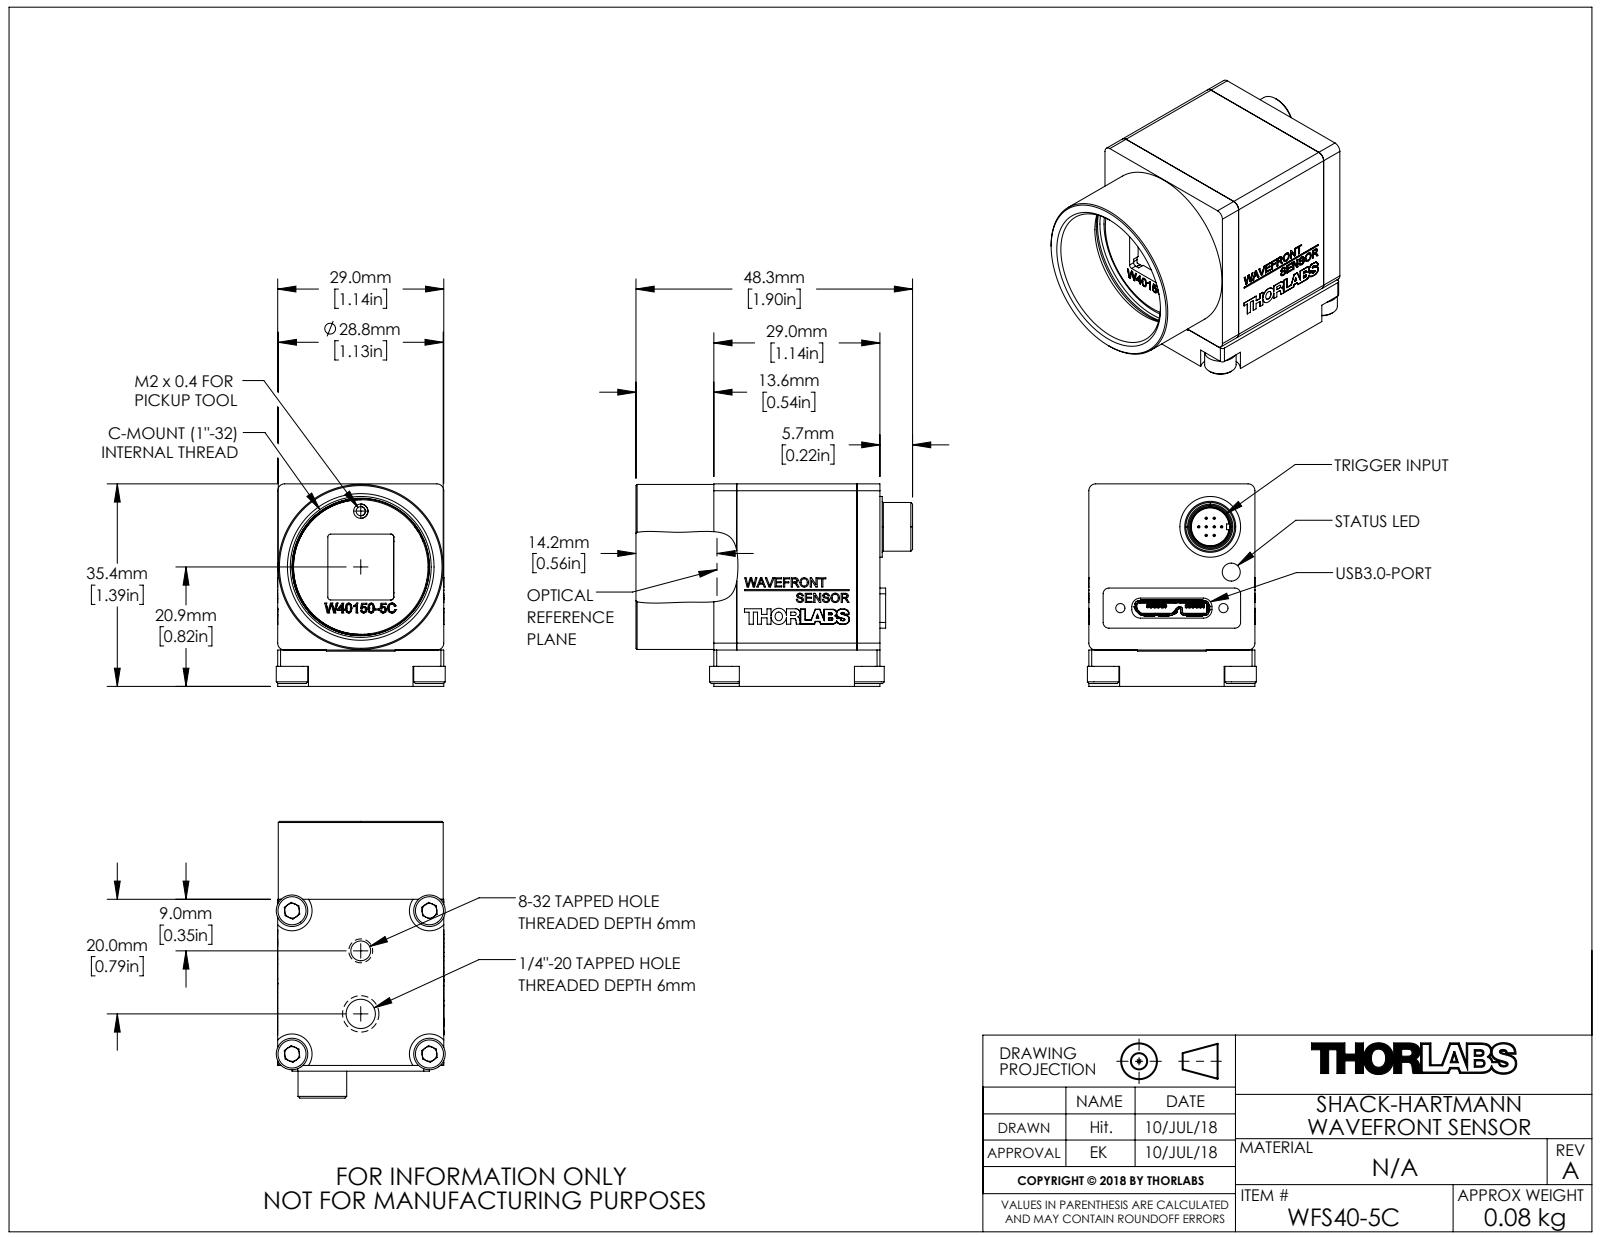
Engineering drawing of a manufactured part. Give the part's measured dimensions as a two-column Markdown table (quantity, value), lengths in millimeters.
| quantity | value |
| --- | --- |
| part name | 20.04.28_MTN008529 WFS40-5C WEB |
| STEP written by | SolidWorks 2018 (AUTOMOTIVE_DESIGN) |
| units | millimeters |
| bodies | 24 solids, 1959 faces (1506 planar, 208 cylindrical, 245 other) |
| overall size | 48.3 × 35.35 × 29.5 |
| volume | 18 135 mm³ |
| surface area | 20 446 mm² |
| round holes (diameter × count) | 3.2 × 11, 2.5 × 5, 1.6 × 3, 1.9 × 3, 1 × 1, 1.5 × 1, 3.3 × 1, 5 × 1, 6.8 × 1, 8 × 1, 24 × 1, 24.6 × 1 |
| round bosses / shafts (diameter × count) | 3 × 11, 0.4 × 8, 5.5 × 4, 28.8 × 1, 23.5 × 1, 15.4 × 1, 10.6 × 1, 8.5 × 1 |
| partial cylindrical surfaces (radius × count) | 0.5 × 27, 1 × 12, 1.5 × 10, 0.6 × 8, 1.8 × 8, 0.2 × 7, 0.1 × 6, 1.2 × 6 |
| main face-to-face distances | 0.6, 29, 28.4, 6.35, 1.2, 16.65, 35.35, 4.8, 27.8, 2.1 |
| hole center spacings | 9.75, 18.83, 9.74, 13.79, 16.88, 5.04, 5.05, 13.89 |
